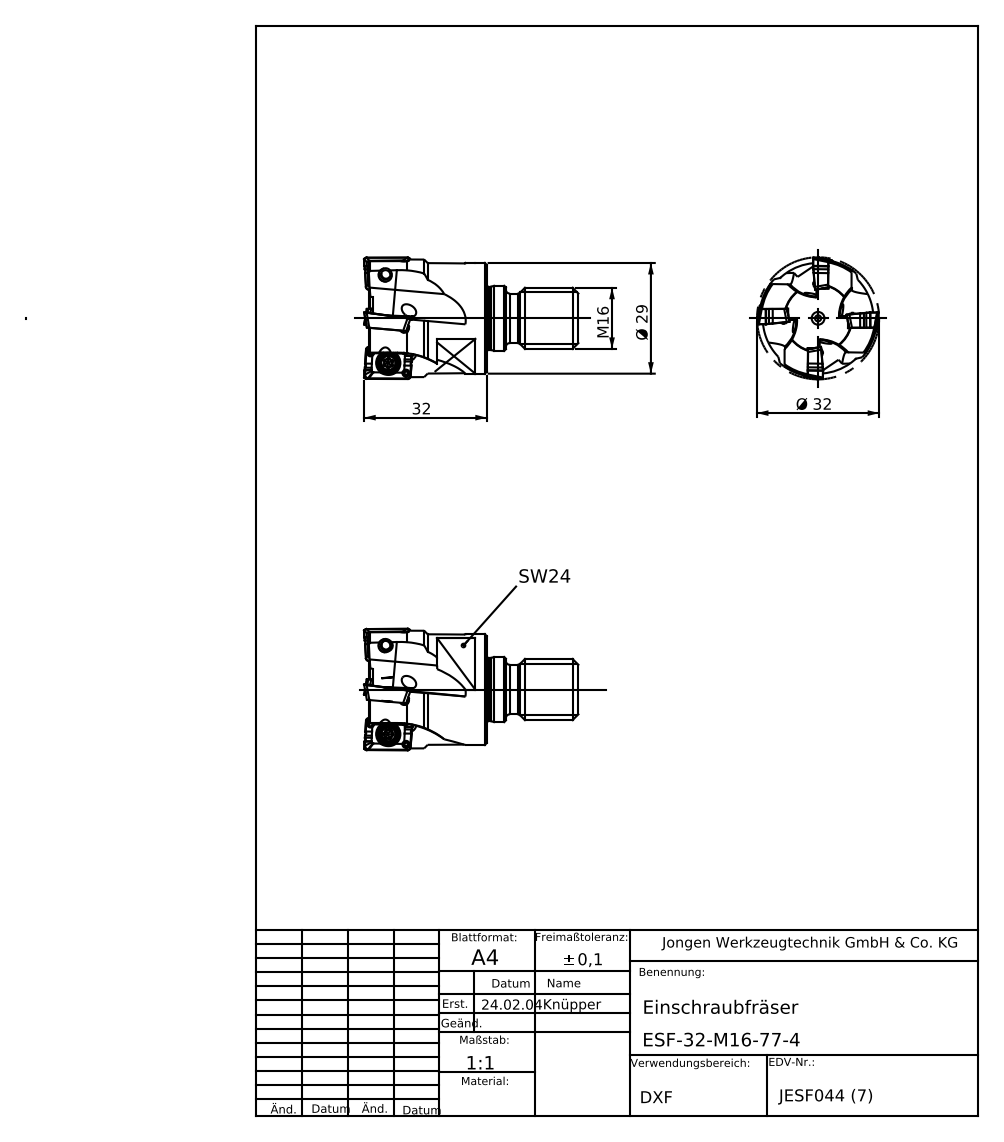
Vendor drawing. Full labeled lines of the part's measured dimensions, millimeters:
Part name (STEP PRODUCT): ESF-32-M16-77-4
STEP written by: SolidWorks 2013 (AUTOMOTIVE_DESIGN)
Units: millimetres
Bodies: 1 solid, 115 faces (54 planar, 39 cylindrical, 22 other)
Overall size (bounding box): 55.99 × 32.03 × 32.03
Volume: 22 570 mm³ · Surface area: 8 188 mm²
Round holes (diameter × count): ⌀3 ×4, ⌀1.6 ×1, ⌀4 ×1
Round bosses / shafts (diameter × count): ⌀29 ×1, ⌀17 ×1, ⌀16.6 ×1, ⌀16 ×1, ⌀13 ×1
Partial cylindrical surfaces — rounded edges, fillets, slot ends (radius × count): R2 ×8, R1.25 ×4, R10 ×4, R21.73 ×4, R15.43 ×1
Main face-to-face distances: 24, 29.9, 53.9, 26.9, 3, 27, 3.1, 16.9, 10, 13
